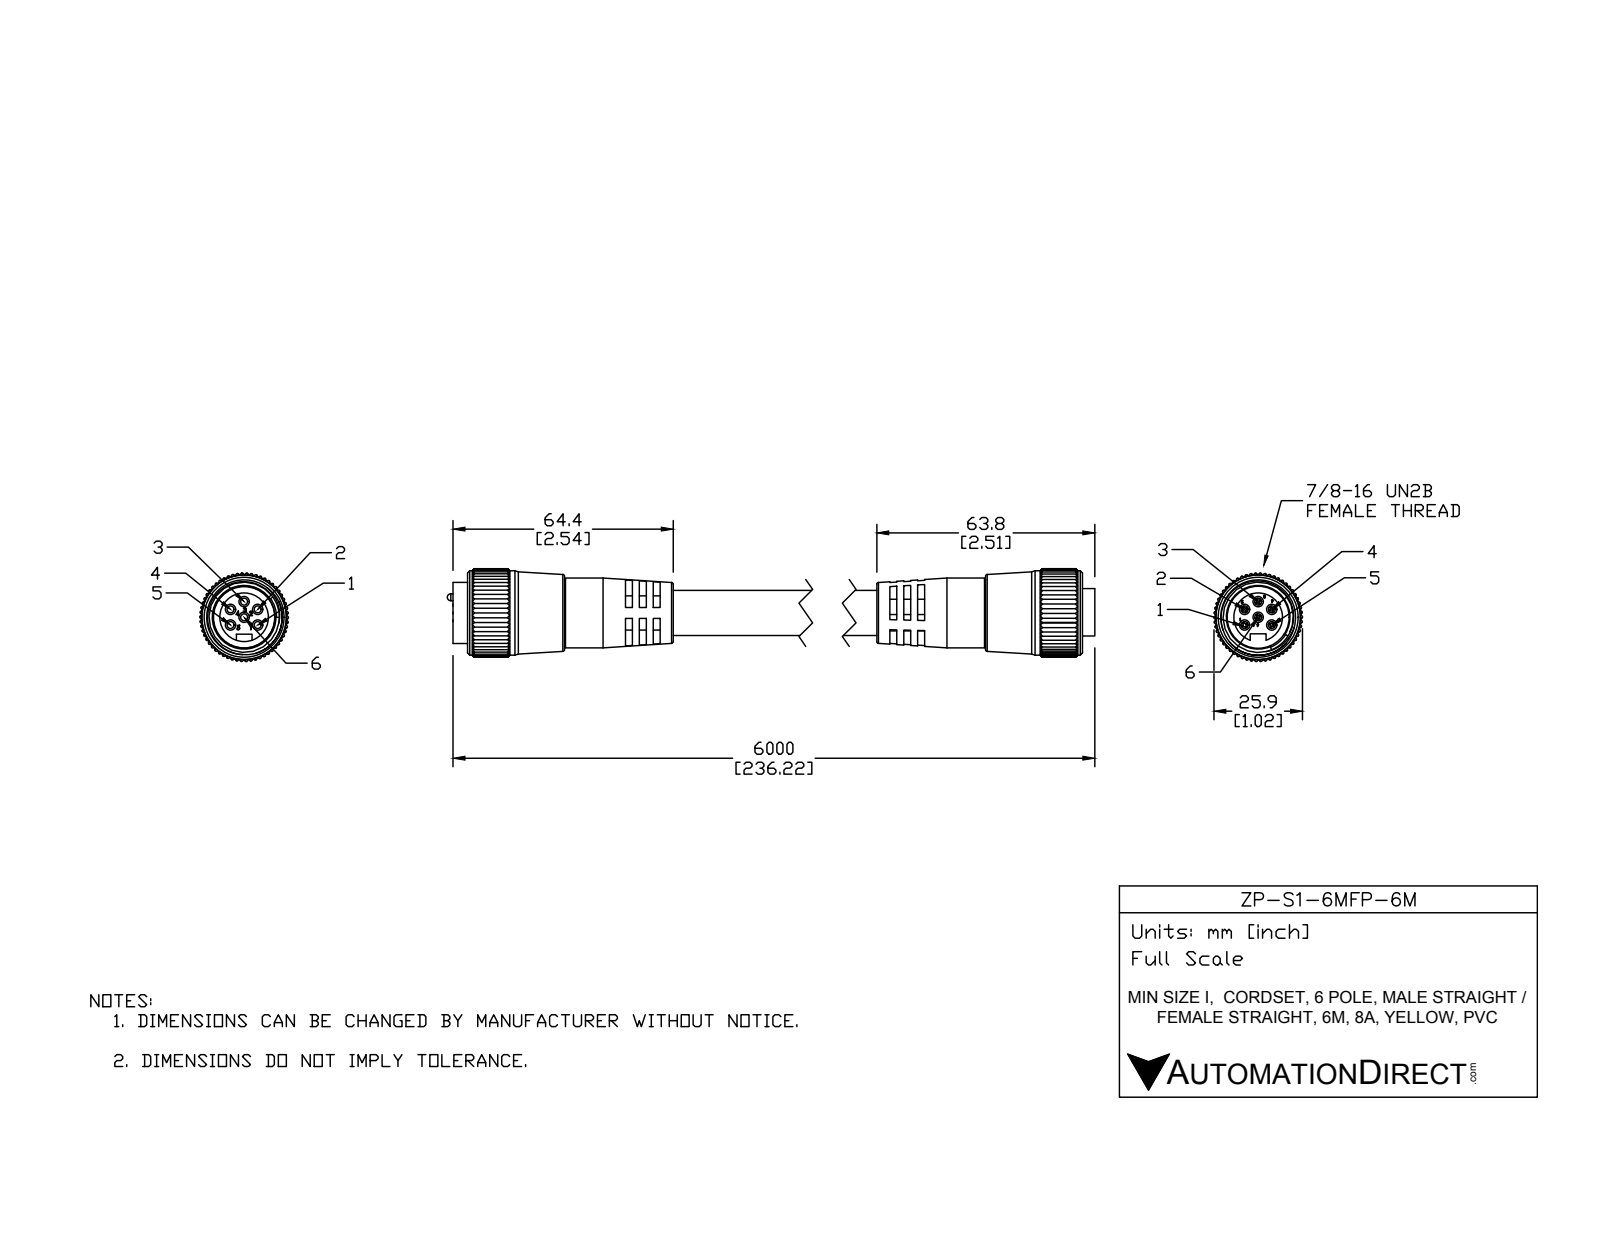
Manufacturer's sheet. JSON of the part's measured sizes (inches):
{"part_name": "ZP-S1-6MFP-6M", "step_written_by": "SolidWorks 2015 (AUTOMOTIVE_DESIGN)", "units": "inches", "bodies": {"solids": 10, "faces": 1226, "planar": 452, "cylindrical": 636, "other": 138}, "overall_size": [9.042, 1.017, 1.017], "volume_in3": 3.105, "surface_area_in2": 36.42, "round_holes": [[0.12, 6], [0.786, 1], [0.805, 1], [0.827, 1]], "round_bosses_or_shafts": [[0.079, 6], [0.972, 1], [0.803, 1], [0.768, 1], [0.704, 1], [0.56, 1], [0.39, 1], [0.12, 1]], "partial_cylinders_radius": [[0.01, 165], [0.09, 1], [0.207, 1], [0.509, 1]], "face_to_face_distances": [0.079, 0.158, 4.633, 4.474, 0.159, 4.95, 2.356, 0.159, 4.791, 4.792], "hole_center_spacings": [0.18, 0.18, 0.311, 0.312, 0.36]}
